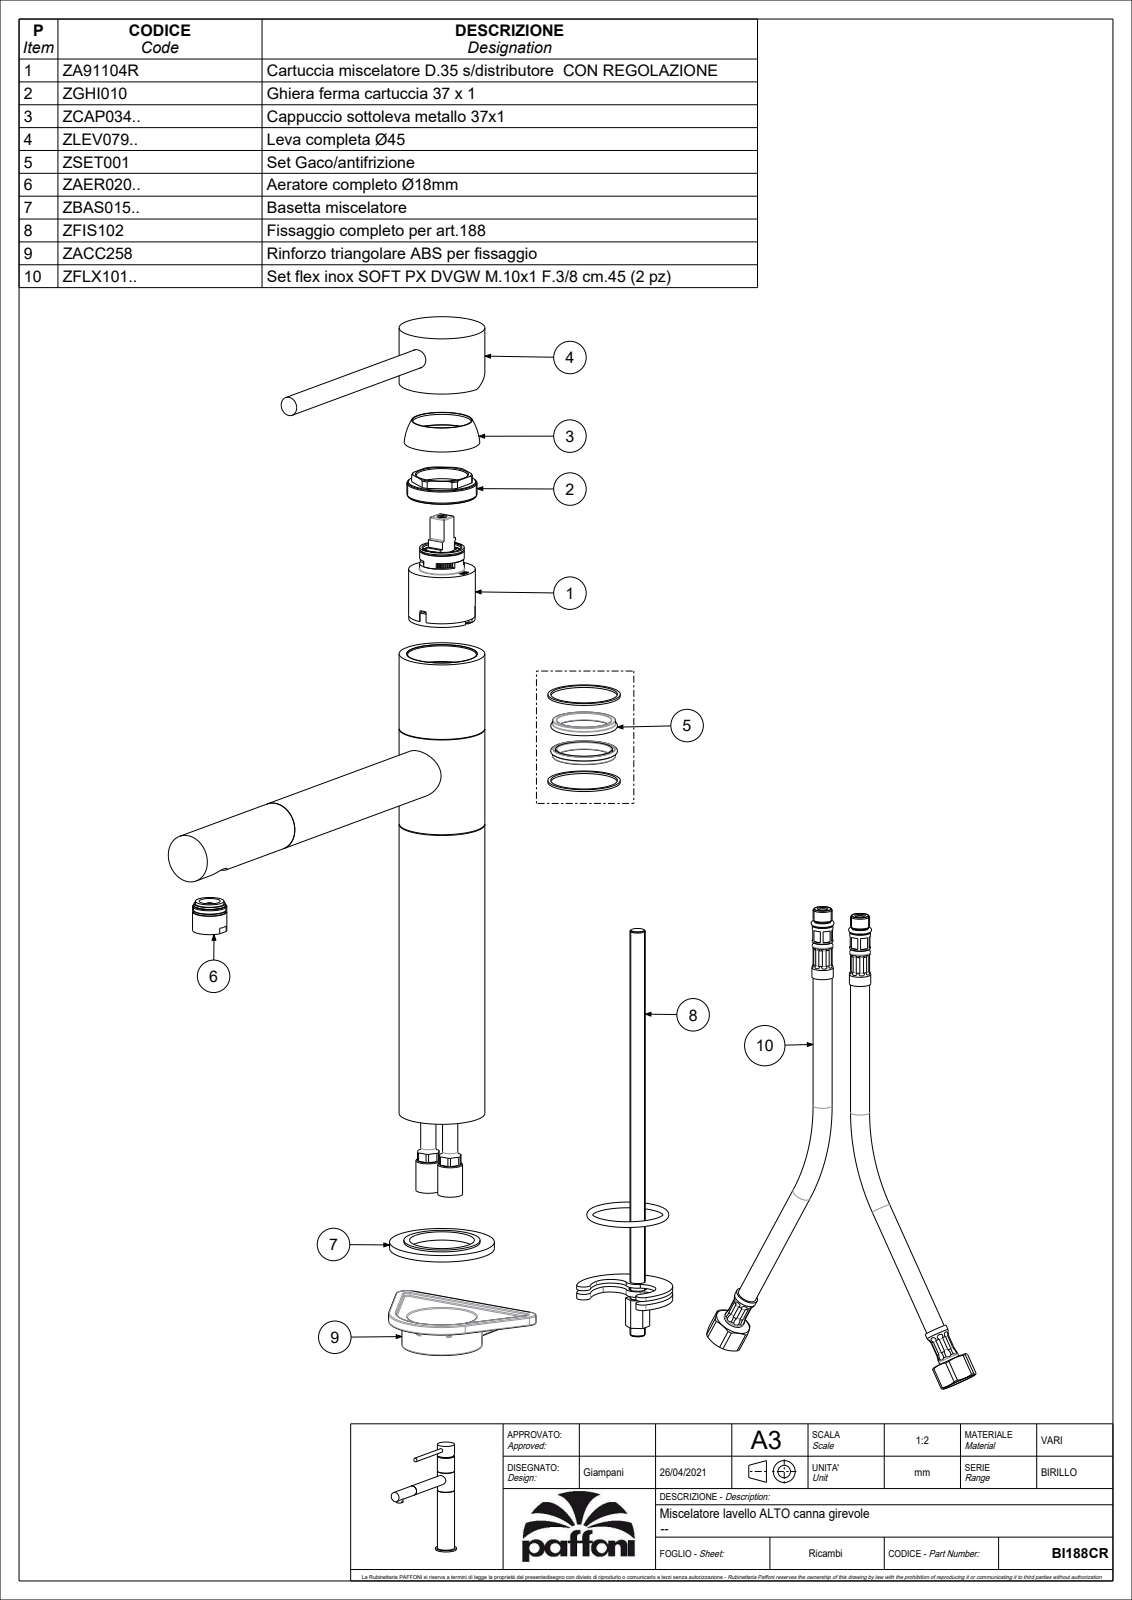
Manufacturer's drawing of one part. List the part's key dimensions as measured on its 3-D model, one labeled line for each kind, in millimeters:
Part name (STEP PRODUCT): BI188CR
STEP written by: CREO PARAMETRIC BY PTC INC, 2020044 (CONFIG_CONTROL_DESIGN)
Units: millimetres
Bodies: 2 solids, 1132 faces (626 planar, 323 cylindrical, 183 other)
Overall size (bounding box): 285.8 × 260.22 × 55
Volume: 290 272 mm³ · Surface area: 145 905 mm²
Round holes (diameter × count): ⌀9 ×6, ⌀11 ×4, ⌀4 ×3, ⌀8 ×3, ⌀18.4 ×2, ⌀3.3 ×1, ⌀4.5 ×1, ⌀5 ×1, ⌀5.5 ×1, ⌀6.8 ×1, ⌀7.5 ×1, ⌀10 ×1
Round bosses / shafts (diameter × count): ⌀14 ×2, ⌀55 ×1, ⌀45 ×1, ⌀40 ×1, ⌀35 ×1, ⌀34.8 ×1, ⌀32.2 ×1, ⌀32 ×1
Partial cylindrical surfaces — rounded edges, fillets, slot ends (radius × count): R0.5 ×27, R0.15 ×11, R0.3 ×4, R1 ×2, R1.05 ×1, R7 ×1, R9.3 ×1, R10.85 ×1
Main face-to-face distances: 3.5, 4.5, 227, 223.5, 244.2, 14.6, 63.2, 11.7, 1, 212.7
Hole centre spacings: 12, 2.5, 7.43, 8.6, 10.08, 13.46, 14, 14.22
